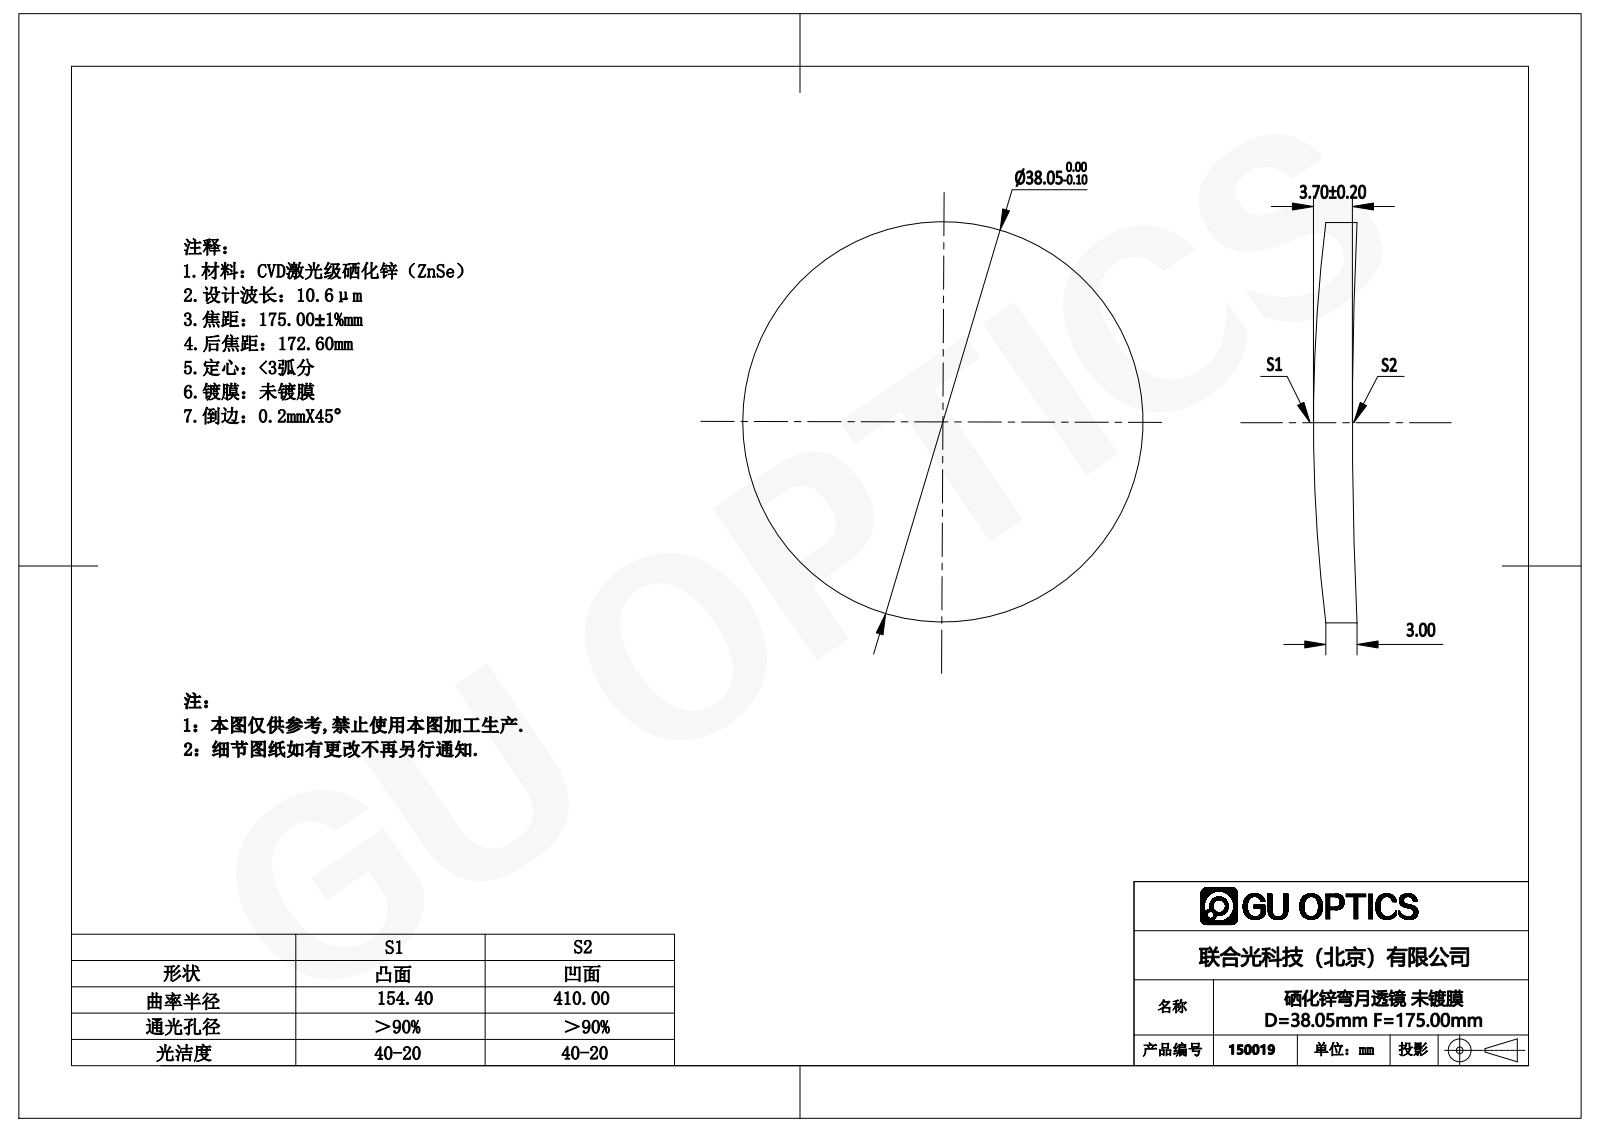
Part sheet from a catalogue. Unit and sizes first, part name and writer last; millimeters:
Units: millimetres
Overall size (bounding box): 38.05 × 38.05 × 4.14
Round bosses / shafts (diameter × count): ⌀38.05 ×1
Volume: 3 790 mm³ · Surface area: 2 634 mm²
Bodies: 1 solid, 6 faces (0 planar, 2 cylindrical, 4 other)
Part name (STEP PRODUCT): 150019
STEP written by: SolidWorks 2016 (AUTOMOTIVE_DESIGN)
